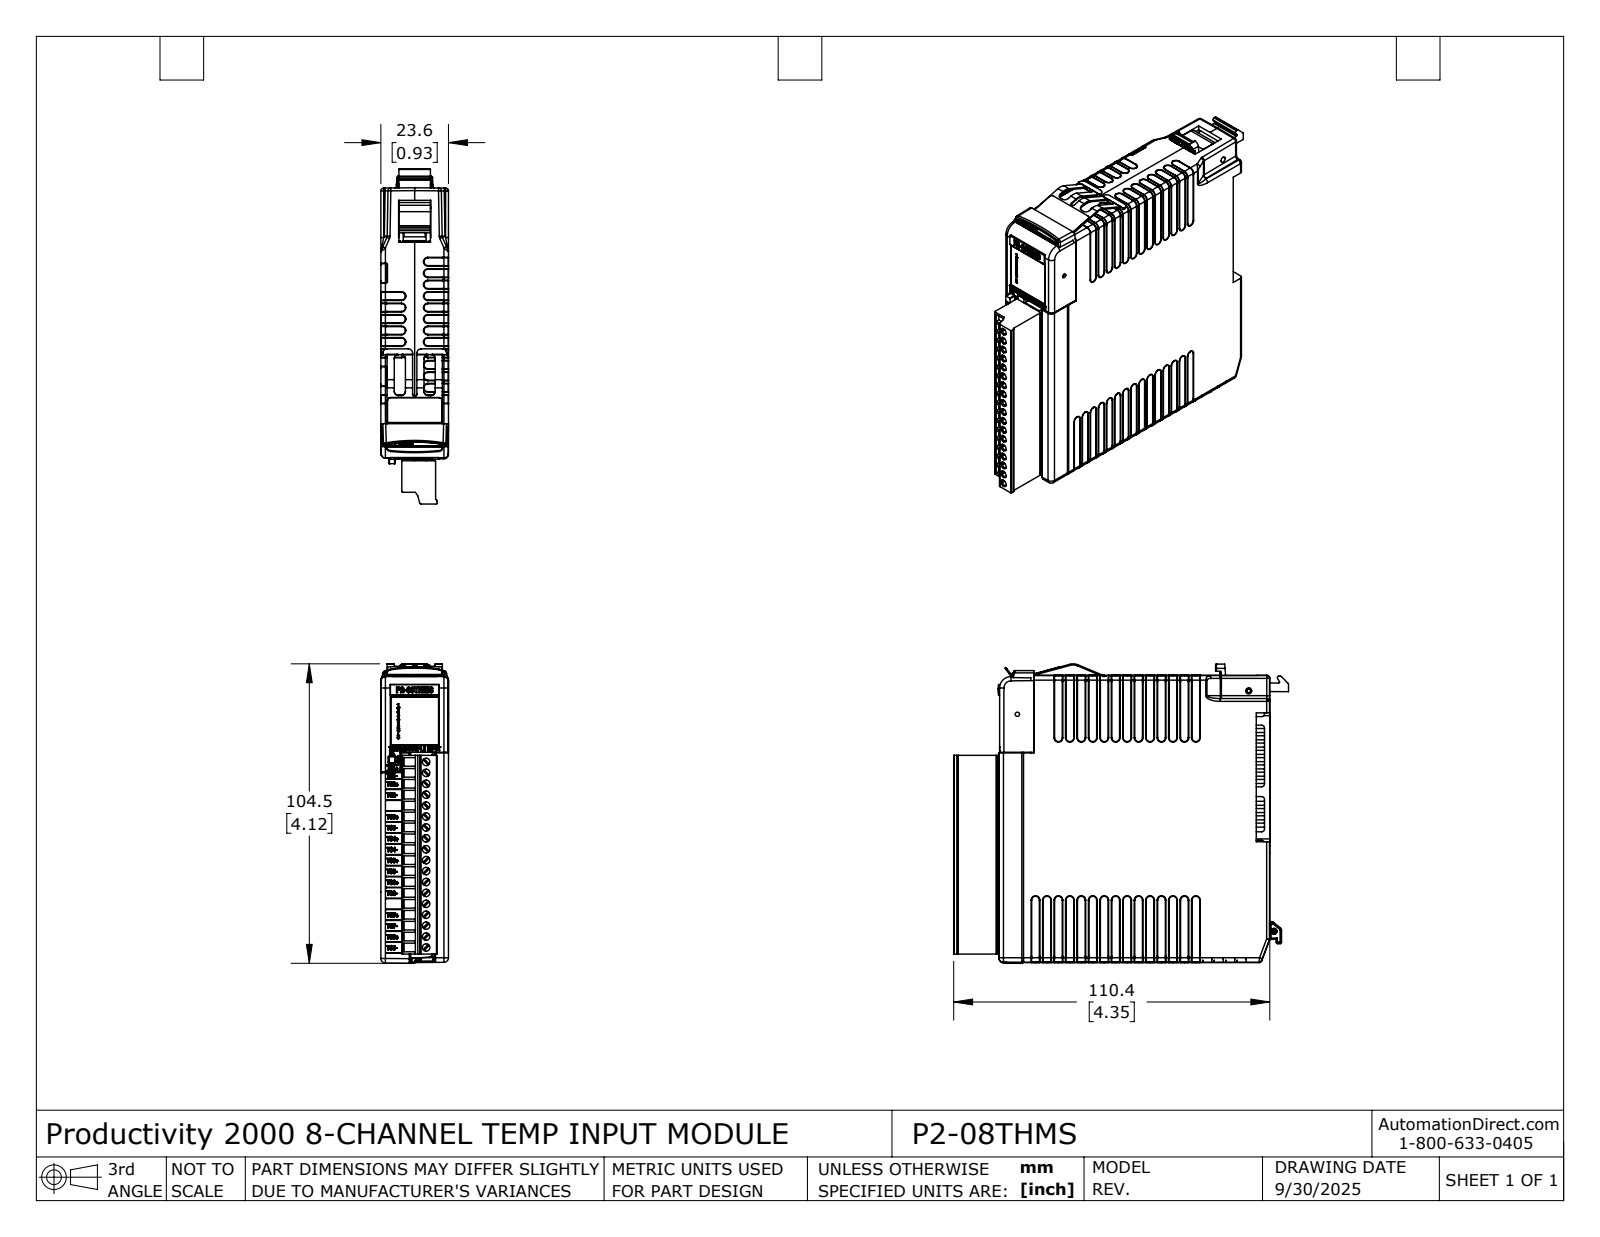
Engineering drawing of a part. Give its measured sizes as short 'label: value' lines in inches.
name: P2-08THMS
written by: SolidWorks 2024 (AUTOMOTIVE_DESIGN)
unit: in
bodies: 11 solids, 5333 faces (2985 planar, 1143 cylindrical, 1205 other)
size: 4.604 × 4.116 × 0.93
volume: 13.16 in³; area: 81.03 in²
holes: 31× ⌀0.063, 18× ⌀0.102, 3× ⌀0.049, 1× ⌀0.059, 1× ⌀0.079, 1× ⌀0.083, 1× ⌀0.098
rounds: 350× R0.02, 77× R0.008, 74× R0.039, 40× R0.059, 36× R0.004, 18× R0.055, 18× R0.062, 18× R0.065
face distances: 0.93, 0.063, 0.867, 0.928, 0.927, 0.928, 0.221, 0.707, 0.706, 0.222
hole spacings: 0.6, 0.15, 0.3, 0.45, 0.168, 1.2, 0.309, 0.75
